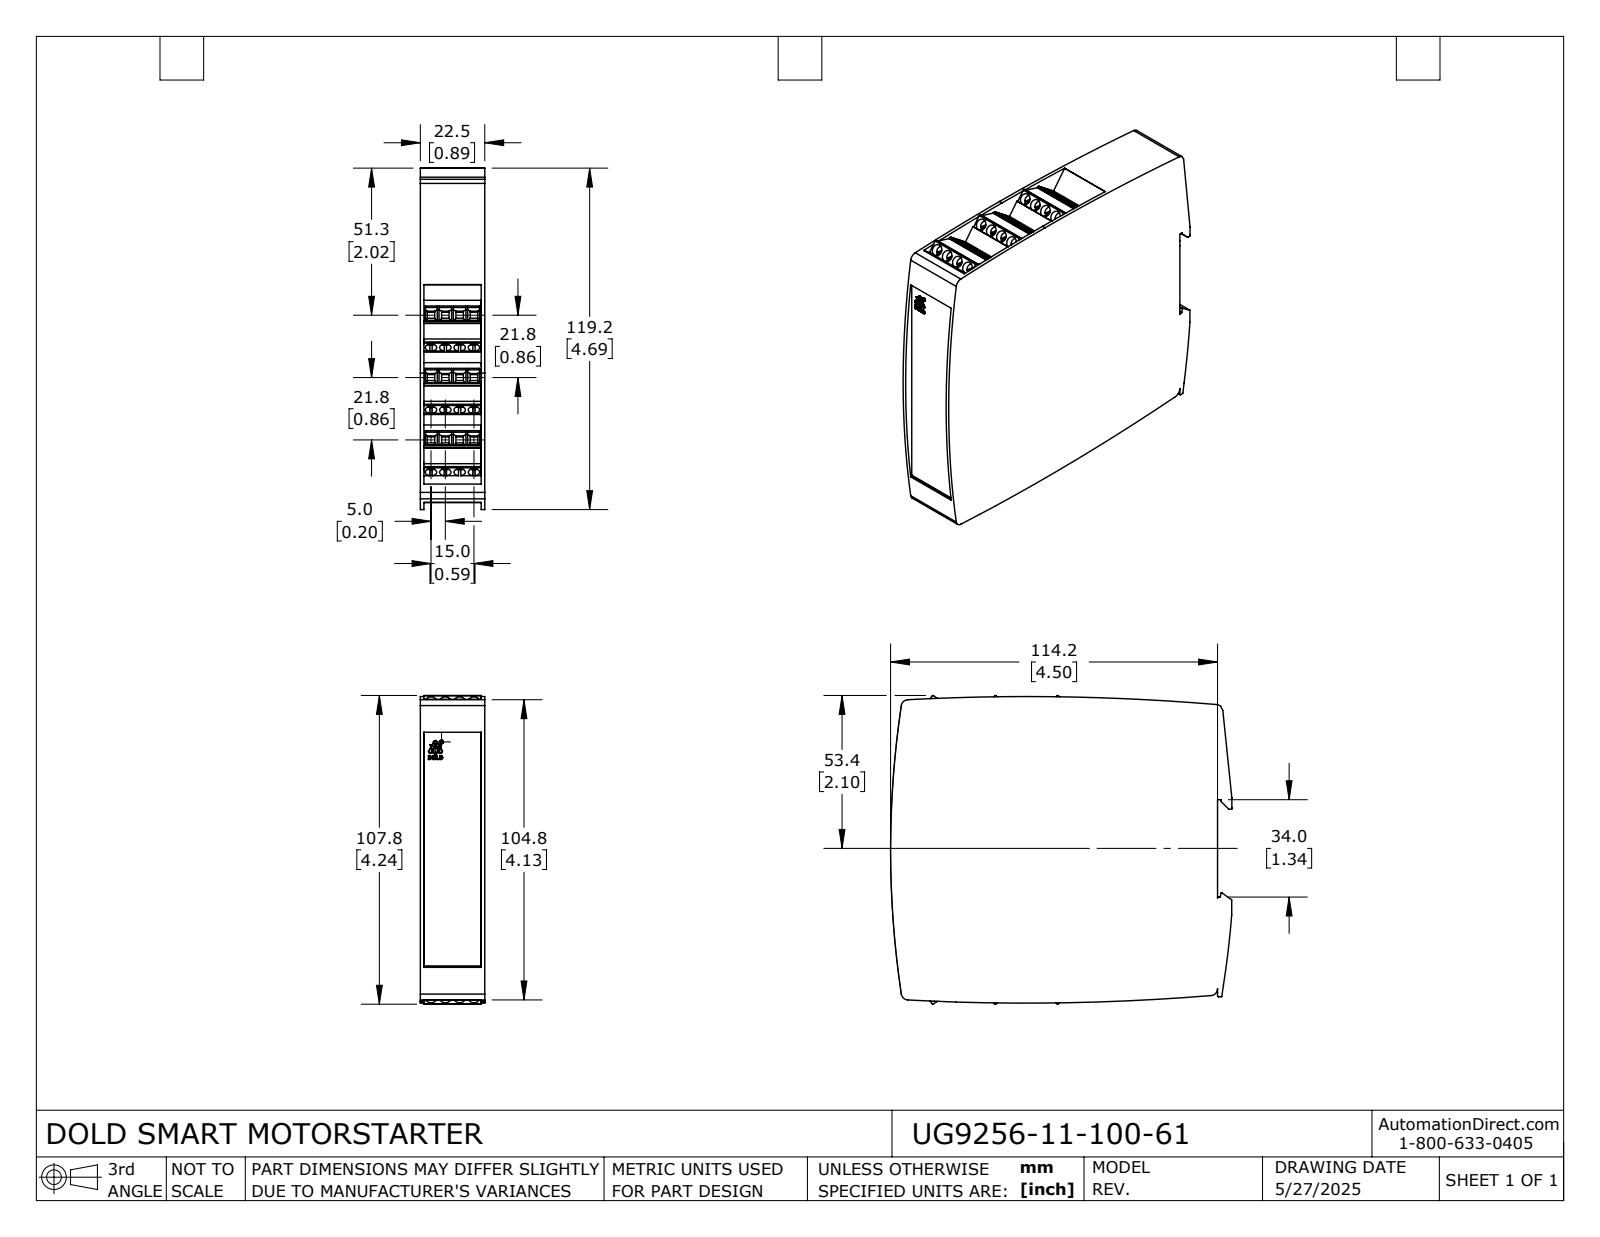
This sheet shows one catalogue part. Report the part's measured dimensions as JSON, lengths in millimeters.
{"part_name": "UG9256-11-100-61", "step_written_by": "SolidWorks 2024 (AUTOMOTIVE_DESIGN)", "units": "millimeters", "bodies": {"solids": 1, "faces": 1036, "planar": 813, "cylindrical": 222, "other": 1}, "overall_size": [119.2, 107.8, 22.5], "volume_mm3": 259700, "surface_area_mm2": 41750, "round_holes": [[4, 24], [1.3, 1]], "round_bosses_or_shafts": [[3.8, 24], [1.2, 1]], "partial_cylinders_radius": [[0.3, 15], [0.5, 14], [0.1, 12], [2.4, 7], [0.1, 6], [0.1, 4], [800, 4], [0.5, 3]], "face_to_face_distances": [22.5, 1.2, 21.3, 17.1, 111.2, 1.3, 21.2, 34.3, 13.4, 19.9], "hole_center_spacings": [14.3, 5, 13.4, 16.7, 10, 27.3, 20.1, 26.8]}
